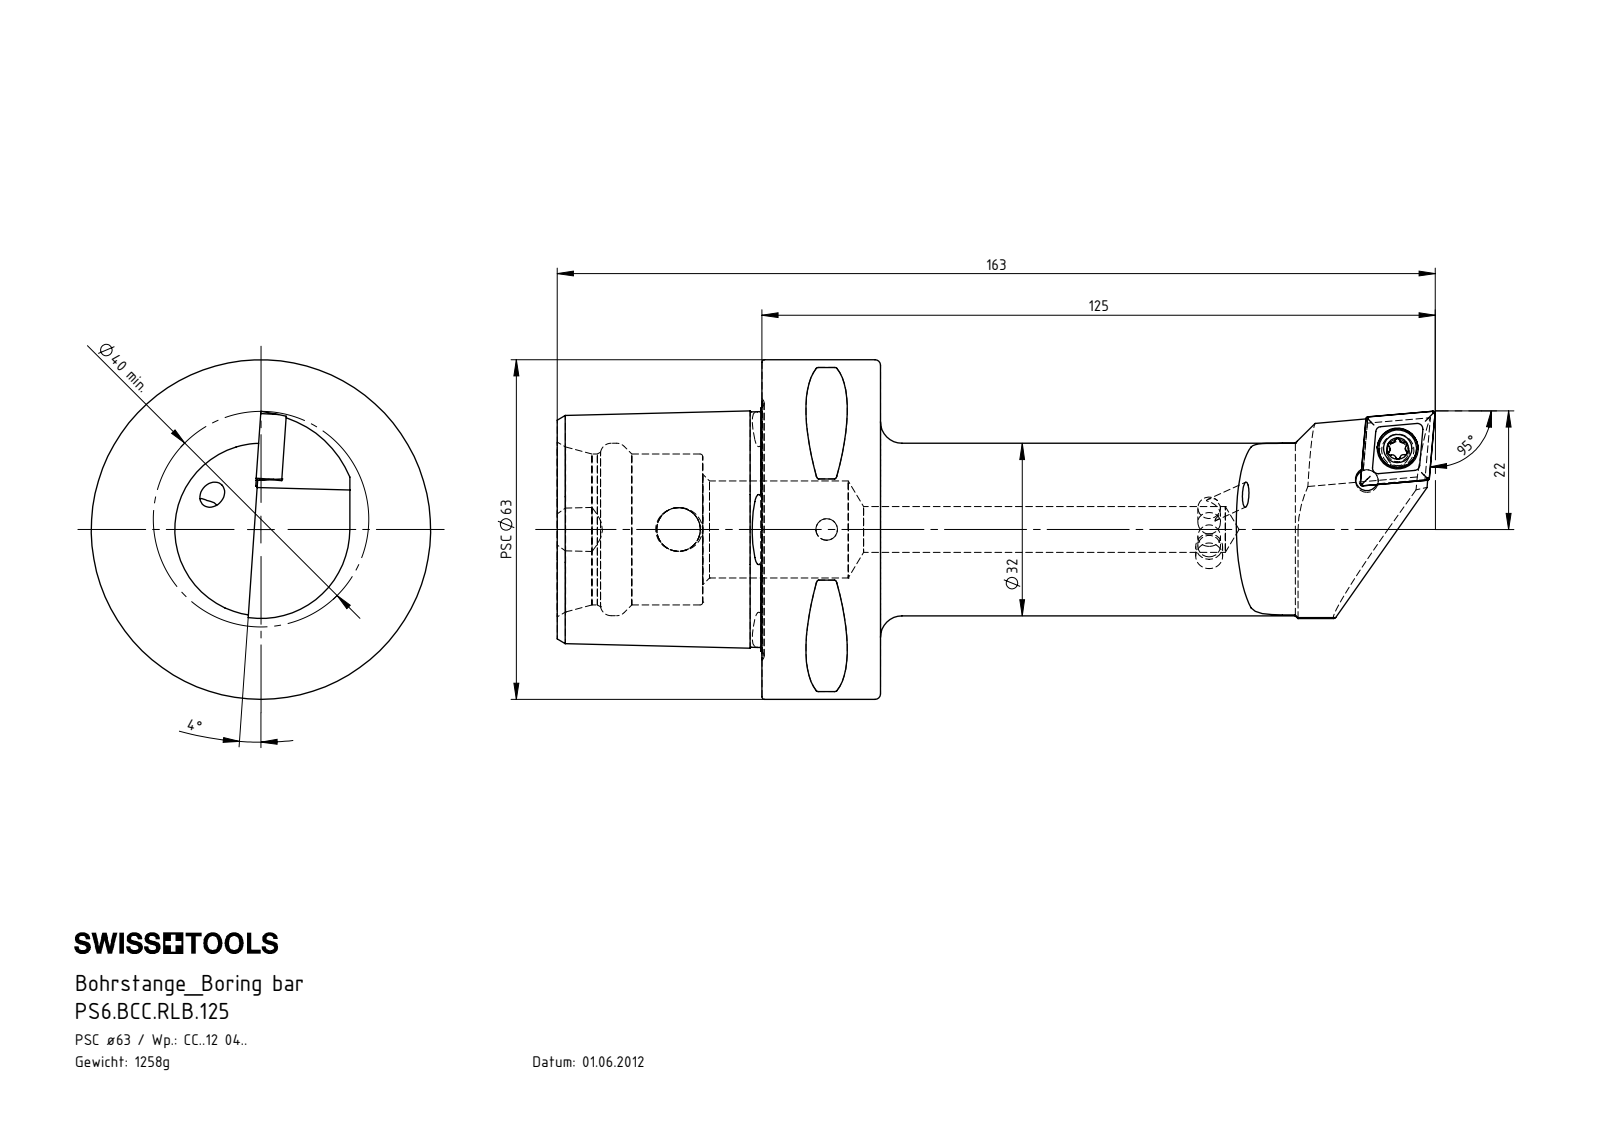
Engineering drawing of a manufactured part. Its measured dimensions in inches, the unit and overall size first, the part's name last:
Units: inches
Overall size (bounding box): 6.416 × 2.48 × 2.48
Round holes (diameter × count): ⌀0.165 ×4, ⌀0.157 ×2, ⌀0.217 ×1, ⌀0.299 ×1, ⌀0.319 ×1, ⌀0.335 ×1, ⌀0.709 ×1, ⌀1.102 ×1, ⌀1.26 ×1
Round bosses / shafts (diameter × count): ⌀0.197 ×2, ⌀2.48 ×1, ⌀0.276 ×1
Partial cylindrical surfaces — rounded edges, fillets, slot ends (radius × count): R0.02 ×8, R0.015 ×6, R0.027 ×3, R0.027 ×3, R0.118 ×1, R0.236 ×1, R0.65 ×1, R0.748 ×1
Main face-to-face distances: 0.866, 1.496, 2.362, 0.98, 1.063, 0.433, 1.299, 0.175, 2.197, 1.488
Hole centre spacings: 0.313, 0.319, 1.083
Volume: 9.86 in³ · Surface area: 50.4 in²
Bodies: 5 solids, 276 faces (49 planar, 74 cylindrical, 153 other)
Part name (STEP PRODUCT): WCC-ER2.001.010_A; CCMT120404; PS6-BCC.RLB.125_A; PS6.BCC.RLB.125 (+1 more)
STEP written by: SolidWorks 2017 (AUTOMOTIVE_DESIGN)
